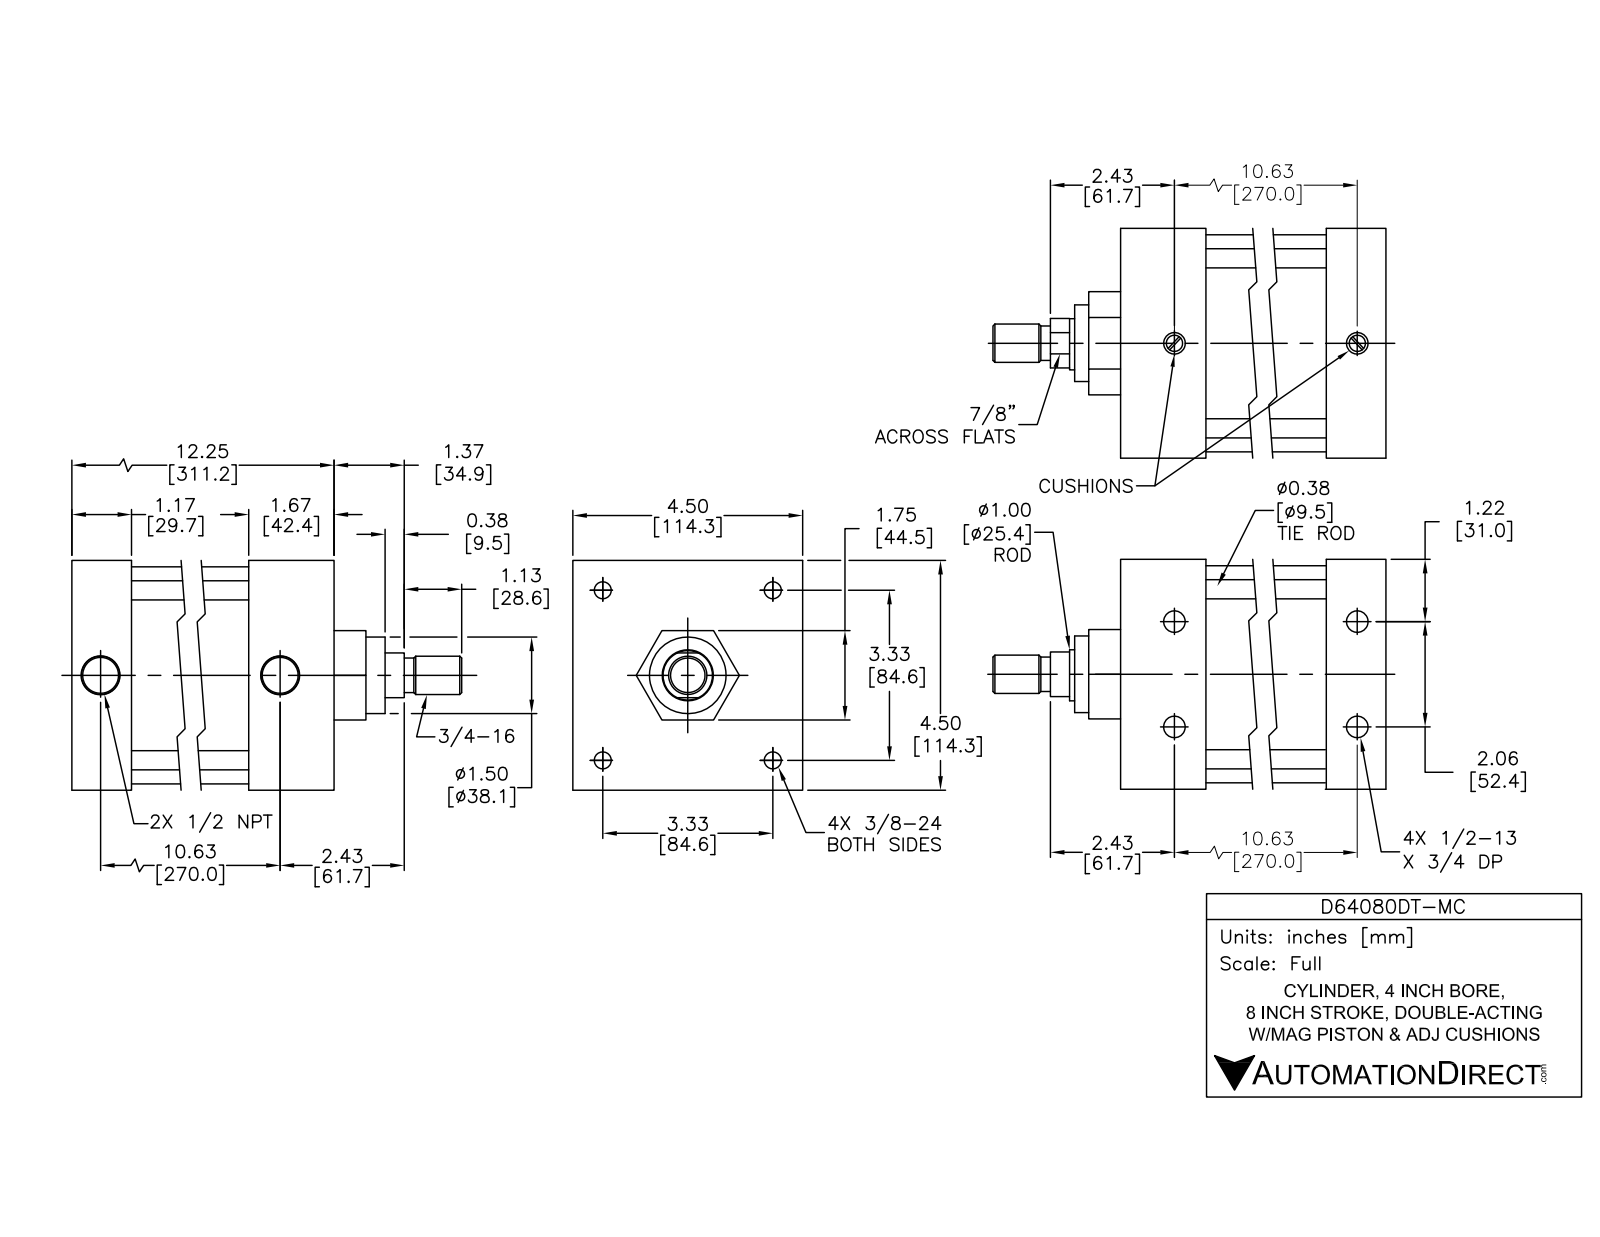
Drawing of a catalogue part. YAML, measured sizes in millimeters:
part_name: "D64080DT-MC; D64080DT-M BODY; D64080DT-M PISTON"
step_written_by: "SolidWorks 2015 (AUTOMOTIVE_DESIGN)"
units: millimeters
bodies: {solids: 12, faces: 303, planar: 99, cylindrical: 114, other: 90}
overall_size: [374.5, 114.3, 114.3]
volume: 1630000
surface_area: 359300
round_holes:
  - {diameter: 8.4, count: 4}
  - {diameter: 10.3, count: 4}
  - {diameter: 10.6, count: 4}
  - {diameter: 15.9, count: 4}
  - {diameter: 12.7, count: 2}
  - {diameter: 19.5, count: 2}
  - {diameter: 25.4, count: 1}
  - {diameter: 25.5, count: 1}
  - {diameter: 101.6, count: 1}
round_bosses_or_shafts:
  - {diameter: 15.5, count: 4}
  - {diameter: 9.5, count: 4}
  - {diameter: 8.6, count: 4}
  - {diameter: 108, count: 1}
  - {diameter: 101.5, count: 1}
  - {diameter: 44.5, count: 1}
  - {diameter: 25.3, count: 1}
  - {diameter: 24.6, count: 1}
partial_cylinders:
  - {radius: 11.4, count: 4}
face_to_face_distances: [114.3, 2, 236.9, 311, 44.5, 279.3, 31.7, 247.7, 31.6, 63.4]
hole_center_spacings: [59.7, 84.4, 271.1, 269.8, 26.2, 26.2, 52.4, 119.3]
